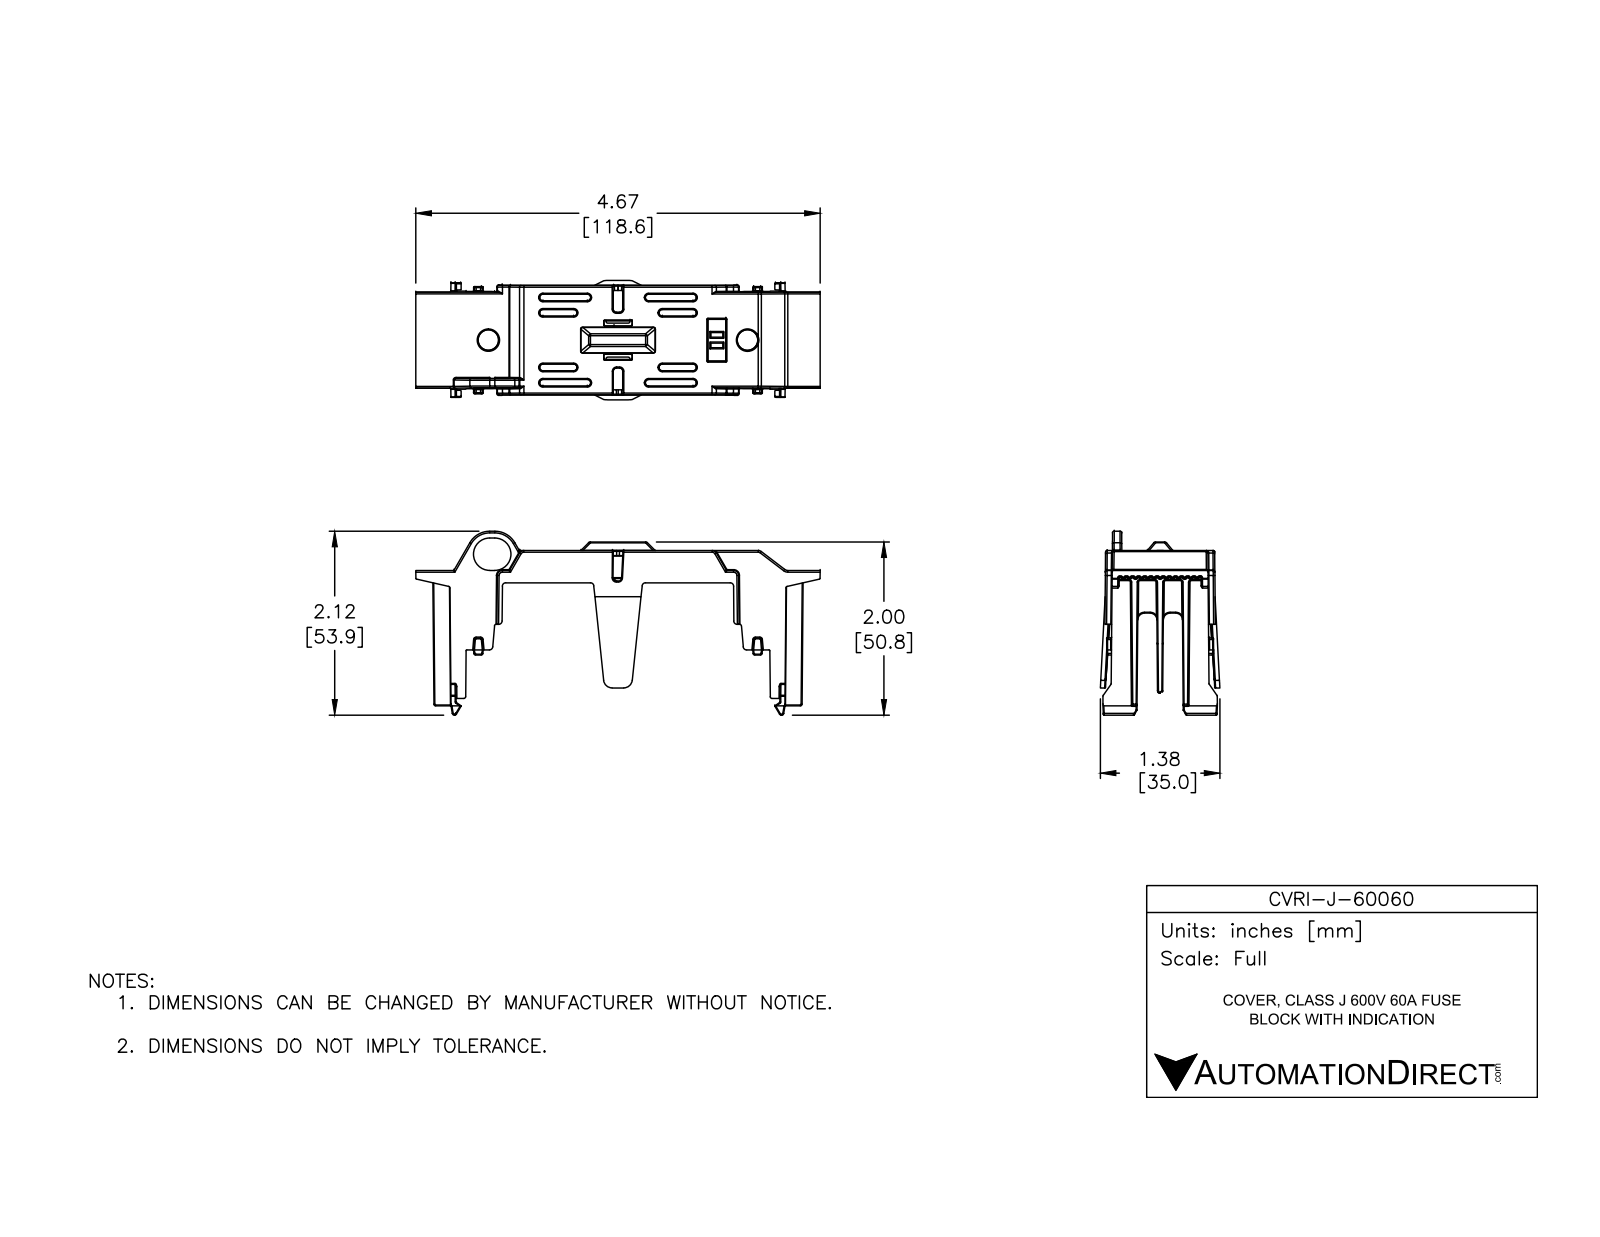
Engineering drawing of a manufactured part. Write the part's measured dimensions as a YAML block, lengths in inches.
part_name: "CVRI-J-60060"
step_written_by: "SolidWorks 2016 (AUTOMOTIVE_DESIGN)"
units: inches
bodies: {solids: 1, faces: 2426, planar: 446, cylindrical: 1066, other: 914}
overall_size: [4.669, 2.123, 1.38]
volume: 1.004
surface_area: 34.28
partial_cylinders:
  - {radius: 0.01, count: 358}
  - {radius: 0.006, count: 177}
  - {radius: 0.02, count: 72}
  - {radius: 0.039, count: 58}
  - {radius: 0.004, count: 27}
  - {radius: 0.03, count: 23}
  - {radius: 0.059, count: 6}
  - {radius: 0.079, count: 4}
face_to_face_distances: [0.059, 0.079, 0.059, 0.23, 0.138, 3.809, 0.171, 0.019, 0.241, 0.3]
